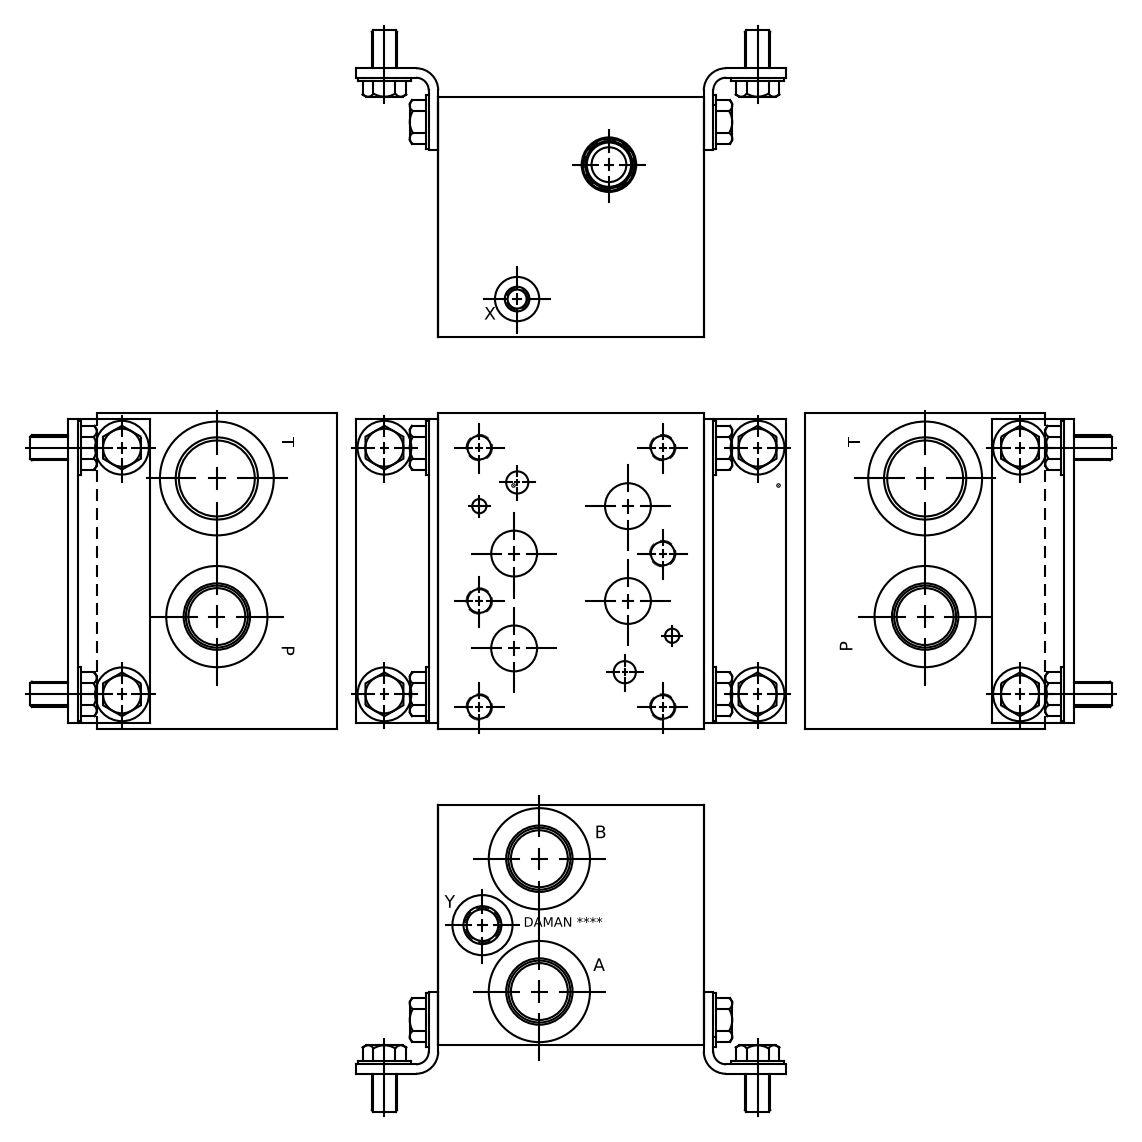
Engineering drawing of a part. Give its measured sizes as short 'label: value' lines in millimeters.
name: Part_AD08P015S~1S_3D
written by: Autodesk Inventor 2021 (AUTOMOTIVE_DESIGN)
unit: mm
bodies: 1 solid, 624 faces (348 planar, 75 cylindrical, 201 other)
size: 158.75 × 133.35 × 120.65
volume: 2 248 000 mm³; area: 158 112 mm²
holes: 8× ⌀10.72, 8× ⌀12.7, 3× ⌀23.01, 3× ⌀31.27, 3× ⌀33.76, 3× ⌀49.12, 2× ⌀7.14, 2× ⌀11.13, 2× ⌀28.57, 2× ⌀33.34, 2× ⌀33.35, 2× ⌀35.51
face distances: 120.65, 133.35, 158.75, 0.79, 132.56, 157.96, 131.77, 19.84, 19.05, 113.51
hole spacings: 29.54, 29.53, 47.62, 53.18, 56.82, 61.92, 74.63, 75.08
